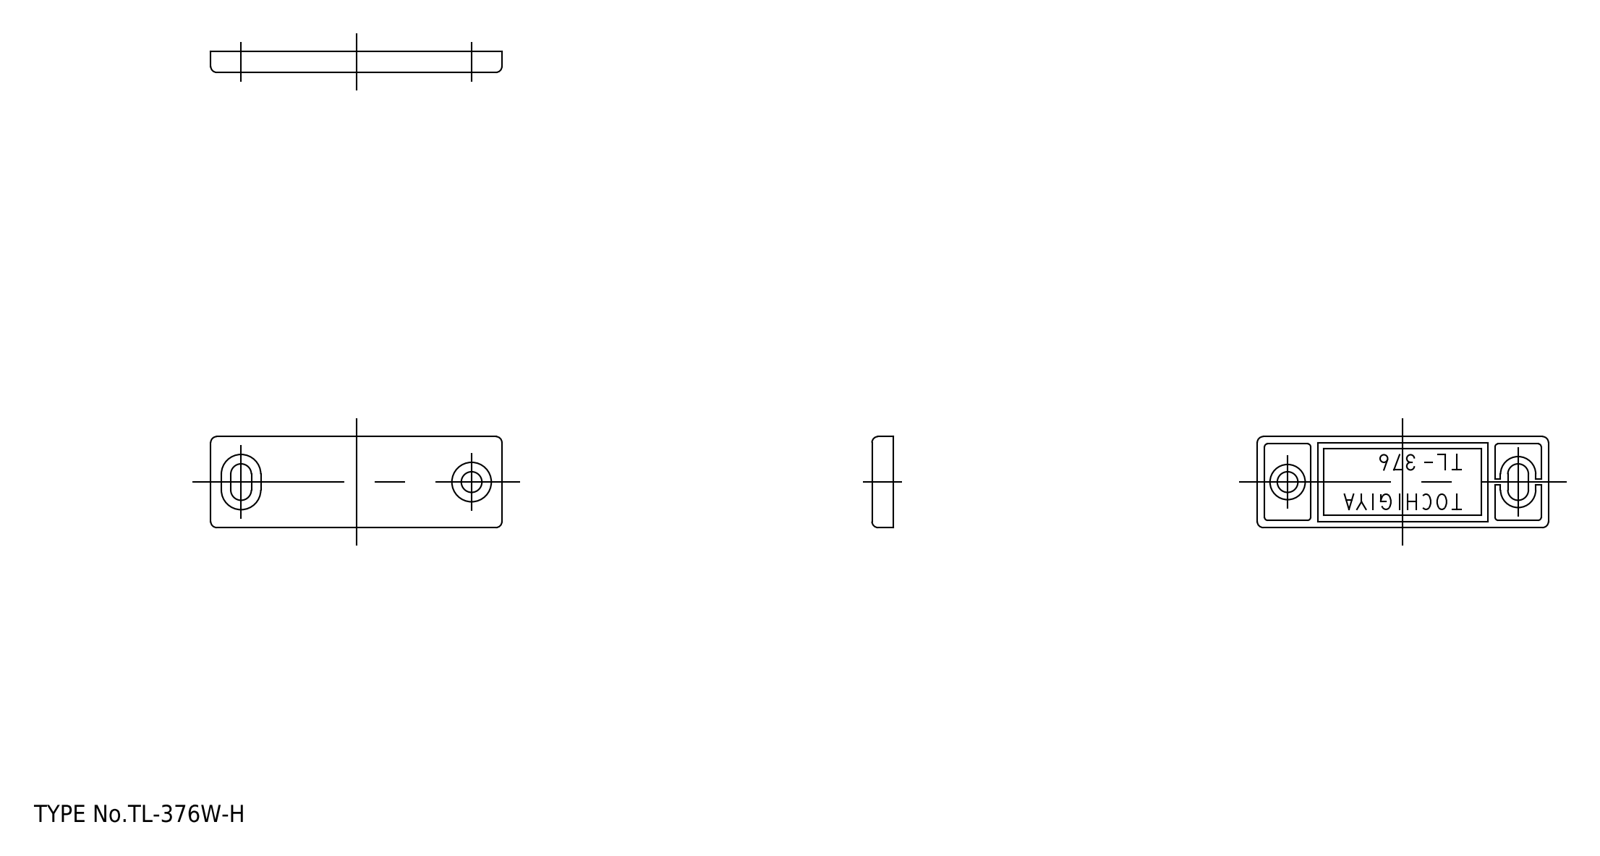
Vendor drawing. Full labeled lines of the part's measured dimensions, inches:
Part name (STEP PRODUCT): TL_376_M1
STEP written by: spGate 19.8.4 (****-****-****-****) (AUTOMOTIVE_DESIGN)
Units: inches
Bodies: 1 solid, 75 faces (47 planar, 18 cylindrical, 10 other)
Overall size (bounding box): 1.89 × 0.591 × 0.138
Volume: 0.125 in³ · Surface area: 3.505 in²
Round bosses / shafts (diameter × count): ⌀0.228 ×1
Partial cylindrical surfaces — rounded edges, fillets, slot ends (radius × count): R0.039 ×8, R0.02 ×4, R0.067 ×2, R0.114 ×2
Main face-to-face distances: 0.13, 0.138, 0.047, 0.079, 0.059, 0.071, 0.591, 0.039, 0.504, 0.346
